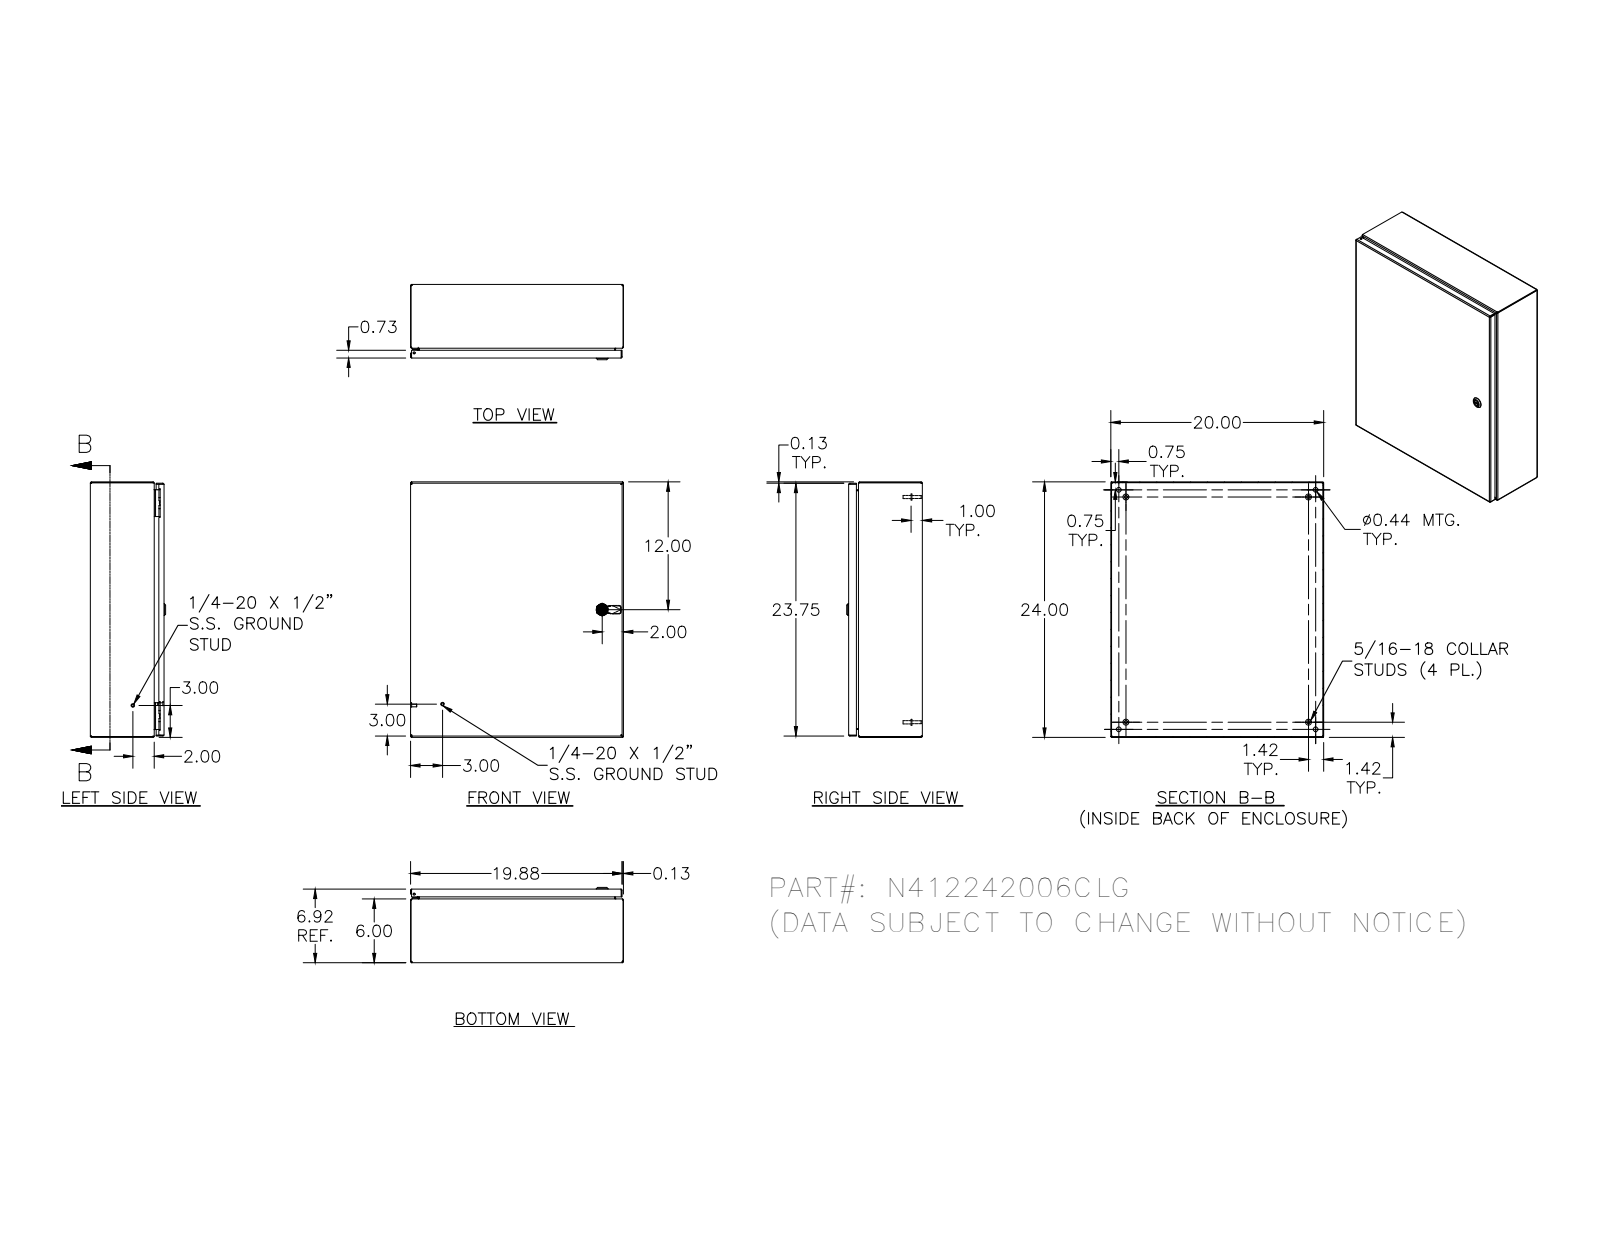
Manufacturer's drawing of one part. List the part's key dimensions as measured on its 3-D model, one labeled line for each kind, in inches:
Part name (STEP PRODUCT): N412242006CLG
STEP written by: SolidWorks 2018 (AUTOMOTIVE_DESIGN)
Units: inches
Bodies: 33 solids, 1449 faces (530 planar, 547 cylindrical, 372 other)
Overall size (bounding box): 24 × 20 × 7.075
Volume: 123.3 in³ · Surface area: 3 350 in²
Round holes (diameter × count): ⌀0.188 ×5, ⌀0.093 ×4, ⌀0.152 ×4, ⌀0.167 ×4, ⌀0.172 ×4, ⌀0.437 ×4, ⌀0.156 ×2, ⌀0.187 ×1, ⌀0.197 ×1, ⌀0.315 ×1, ⌀0.394 ×1, ⌀0.402 ×1
Round bosses / shafts (diameter × count): ⌀0.25 ×10, ⌀0.563 ×4, ⌀0.36 ×4, ⌀0.32 ×4, ⌀0.3 ×4, ⌀0.256 ×4, ⌀0.164 ×4, ⌀0.131 ×4
Partial cylindrical surfaces — rounded edges, fillets, slot ends (radius × count): R0.012 ×30, R0.031 ×30, R0.05 ×26, R0.105 ×20, R0.016 ×18, R0.125 ×16, R0.02 ×13, R0.032 ×8
Main face-to-face distances: 0.074, 6.843, 6.769, 6.917, 0.074, 19.926, 20, 19.852, 19.926, 23.926
Hole centre spacings: 20, 0.66, 0.656, 1.307, 1.965, 19.34, 20.66, 1.619
